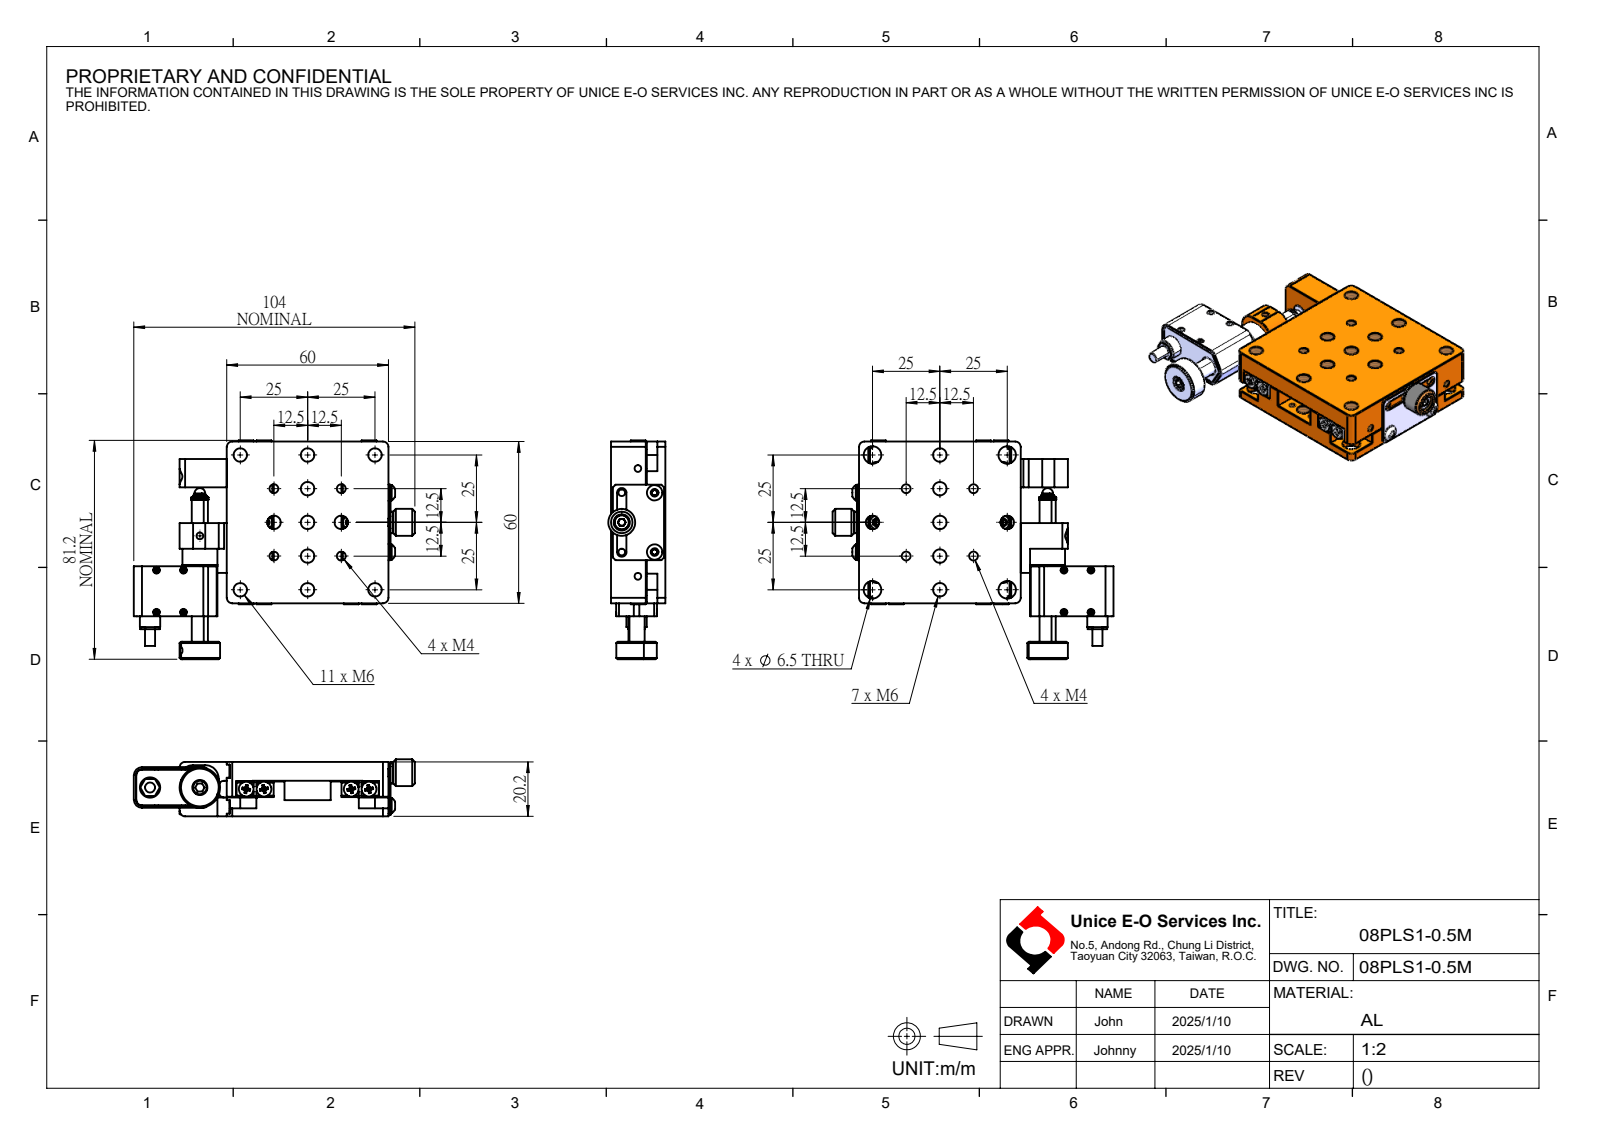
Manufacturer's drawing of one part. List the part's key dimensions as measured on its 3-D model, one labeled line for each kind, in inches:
Part name (STEP PRODUCT): 08PLS1-0.5M
STEP written by: SolidWorks 2024 (CONFIG_CONTROL_DESIGN)
Units: inches
Bodies: 0 solids, 1785 faces (652 planar, 504 cylindrical, 629 other)
Overall size (bounding box): 4.106 × 3.196 × 0.835
Round holes (diameter × count): ⌀0.197 ×26, ⌀0.081 ×20, ⌀0.098 ×18, ⌀0.118 ×13, ⌀0.256 ×7, ⌀0.13 ×4, ⌀0.134 ×3, ⌀0.055 ×2, ⌀0.079 ×2, ⌀0.126 ×2, ⌀0.138 ×2, ⌀0.236 ×2
Round bosses / shafts (diameter × count): ⌀0.118 ×9, ⌀0.217 ×8, ⌀0.236 ×3, ⌀0.224 ×2, ⌀0.079 ×2, ⌀0.055 ×2, ⌀0.591 ×1, ⌀0.394 ×1
Partial cylindrical surfaces — rounded edges, fillets, slot ends (radius × count): R0.079 ×11, R0.197 ×4, R0.236 ×4, R0.069 ×2, R0.118 ×2
Main face-to-face distances: 0.28, 0.516, 0.795, 0.52, 0.276, 0.236, 0.24, 0.031, 0.039, 0.043
Hole centre spacings: 0.984, 0.696, 1.556, 0.787, 1.1, 1.392, 0.394, 0.492
